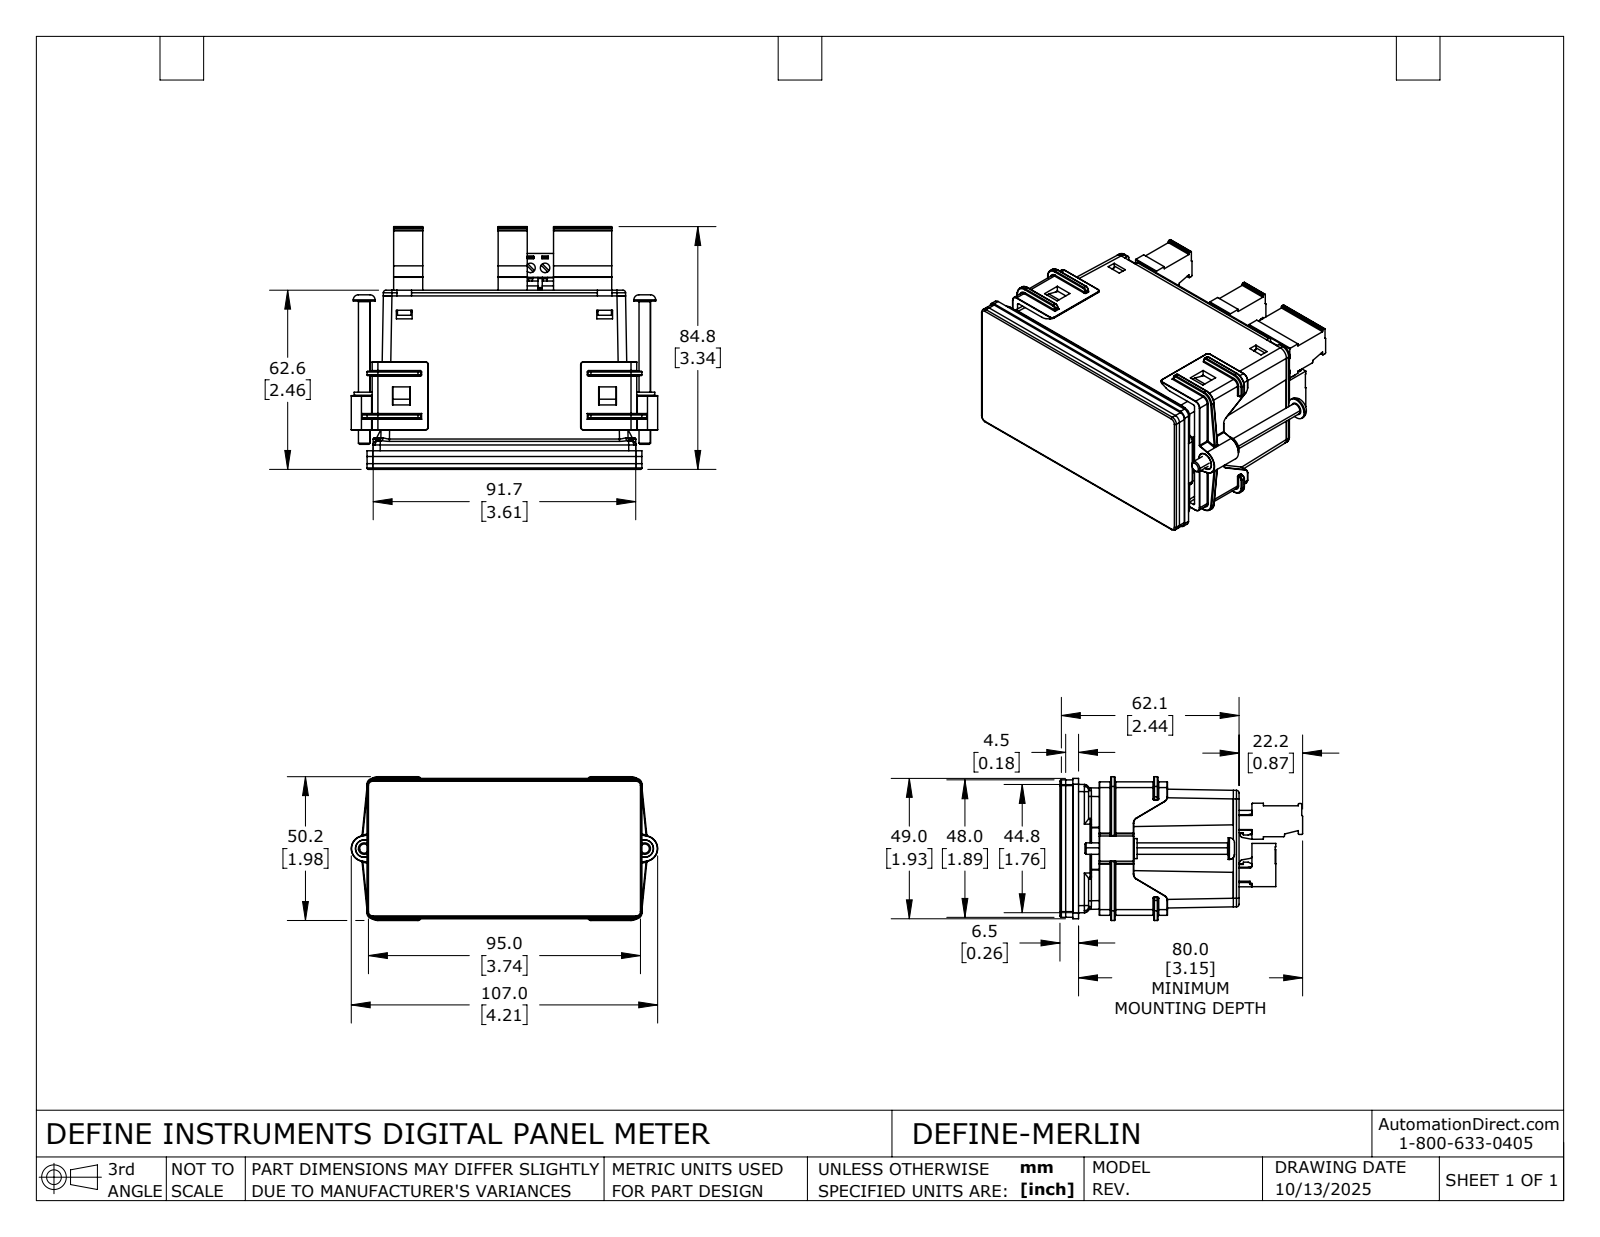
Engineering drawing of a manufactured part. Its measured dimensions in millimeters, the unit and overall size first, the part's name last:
Units: millimetres
Overall size (bounding box): 107 × 84.8 × 50.2
Round holes (diameter × count): ⌀1.2 ×8, ⌀1.5 ×8, ⌀2.4 ×8, ⌀3 ×8, ⌀3.3 ×8, ⌀3.9 ×8, ⌀3.3 ×2, ⌀6.1 ×2, ⌀4.5 ×1
Round bosses / shafts (diameter × count): ⌀7.6 ×2, ⌀7 ×2, ⌀6 ×2, ⌀4 ×2
Partial cylindrical surfaces — rounded edges, fillets, slot ends (radius × count): R0.2 ×136, R0.3 ×100, R0.1 ×49, R0.5 ×46, R0.2 ×37, R0.3 ×32, R1 ×24, R2 ×20
Main face-to-face distances: 2, 39, 2.5, 56.5, 58.5, 4.5, 60.6, 54.1, 56.1, 59.1
Hole centre spacings: 5.1, 10.2, 5.1, 0.4, 15.2, 55.8, 60.9, 66
Volume: 85 790 mm³ · Surface area: 81 870 mm²
Bodies: 20 solids, 5859 faces (4132 planar, 1215 cylindrical, 512 other)
Part name (STEP PRODUCT): DEFINE-MERLIN
STEP written by: SolidWorks 2024 (AUTOMOTIVE_DESIGN)
